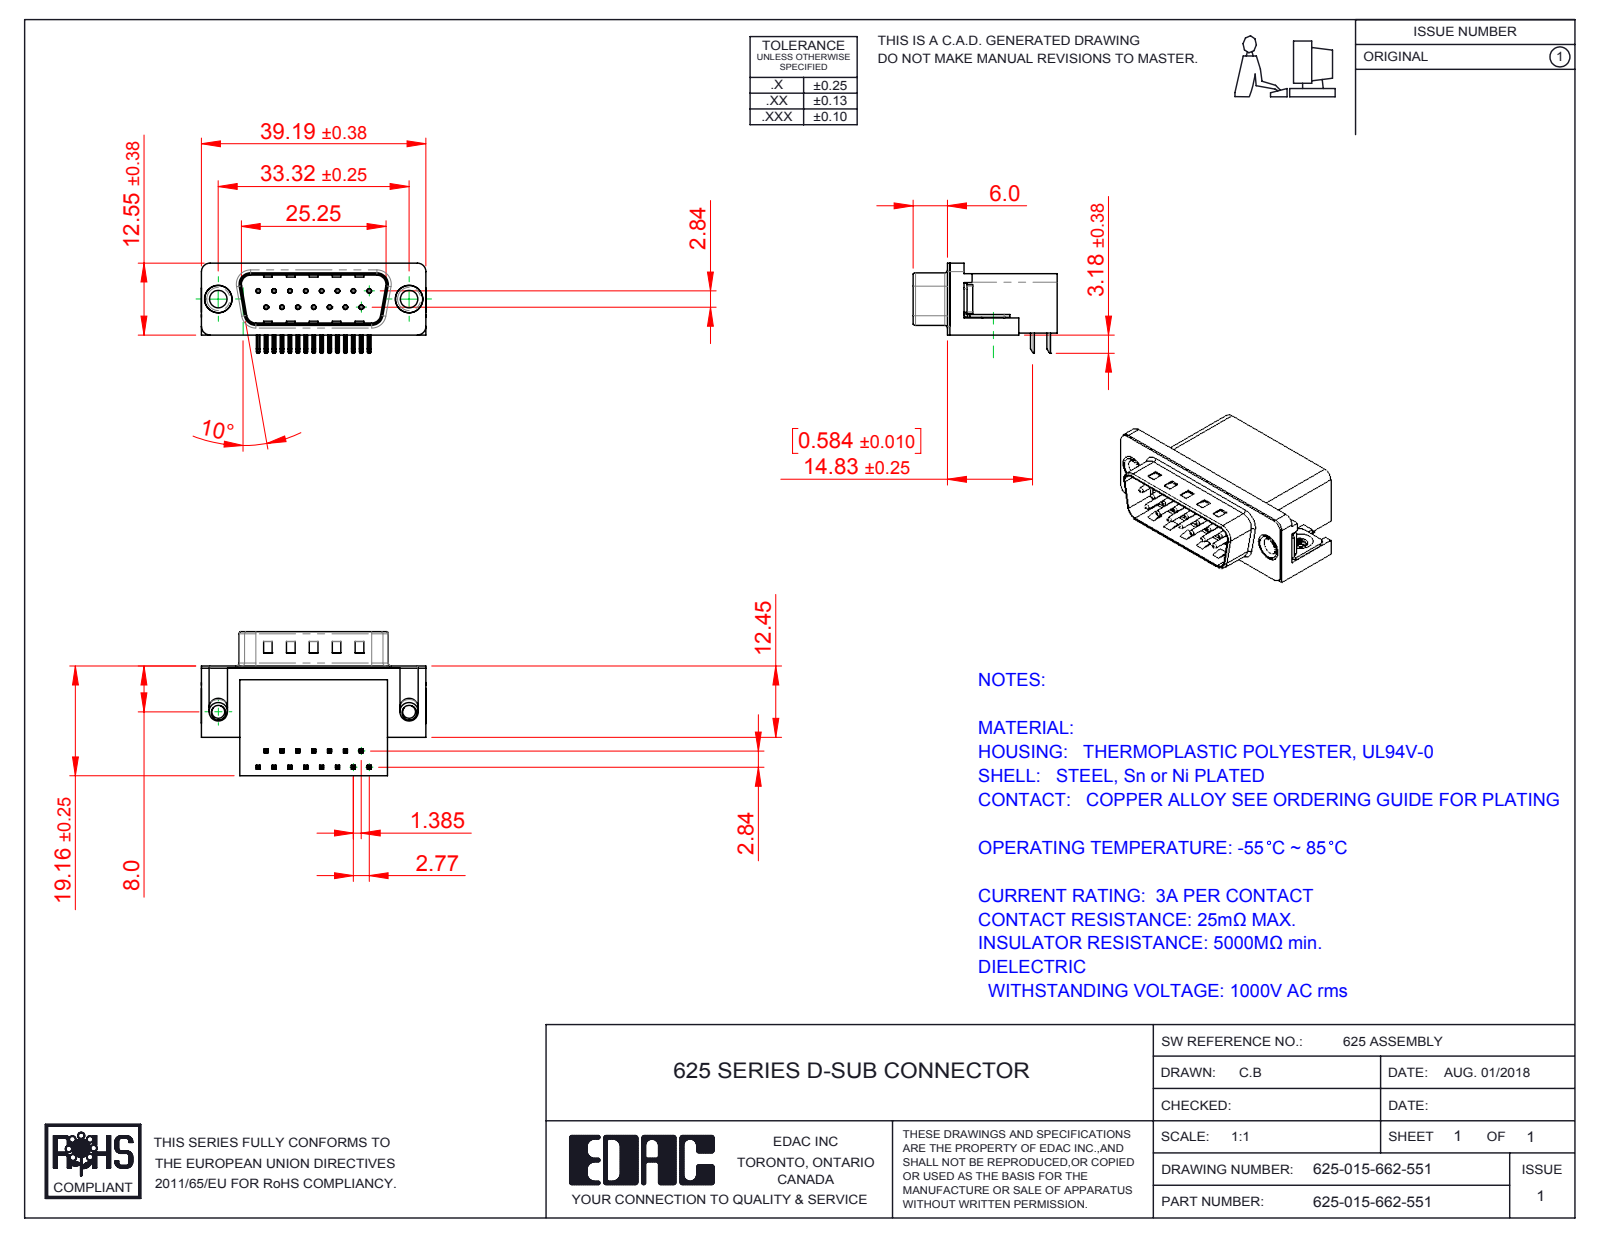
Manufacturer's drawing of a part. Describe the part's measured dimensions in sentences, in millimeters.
The part is named "625 Shell_15 Socket; 625 Contact Top; 625 4-40 Threaded Board Mount; 625 Thru Hole Rivet (+3 more)". Its 3-D file was written by "SolidWorks 2016 (CONFIG_CONTROL_DESIGN)". It is 21 solids with 1471 faces: 895 planar, 441 cylindrical and 135 other. Overall it measures 39.22 by 25.16 by 15.73 millimeters. Its volume is 6 242 cubic millimeters and its surface area 6 480 square millimeters. Round holes: 15 of diameter 0.35, 15 of diameter 0.8, 2 of diameter 2.26, 2 of diameter 3.05, 2 of diameter 4, 2 of diameter 4.8, 2 of diameter 5. Round bosses or shafts: 15 of diameter 0.75, 2 of diameter 4.9, 2 of diameter 4.75, 2 of diameter 3.85, 2 of diameter 3.26. Partial cylindrical surfaces (rounded edges, fillets, slot ends): 68 of radius 0.25, 30 of radius 0.12, 16 of radius 1, 9 of radius 0.5, 8 of radius 1.6, 6 of radius 1.5, 4 of radius 0.9, 4 of radius 2. The main face-to-face distances are 0.4, 10.35, 18.76, 2.1, 19.16, 10.46, 1.7, 10.86, 8.76, 16.26. The hole center spacings are 3.16, 2.77, 5.54, 8.31, 11.08, 5.03, 5.04, 7.48.
